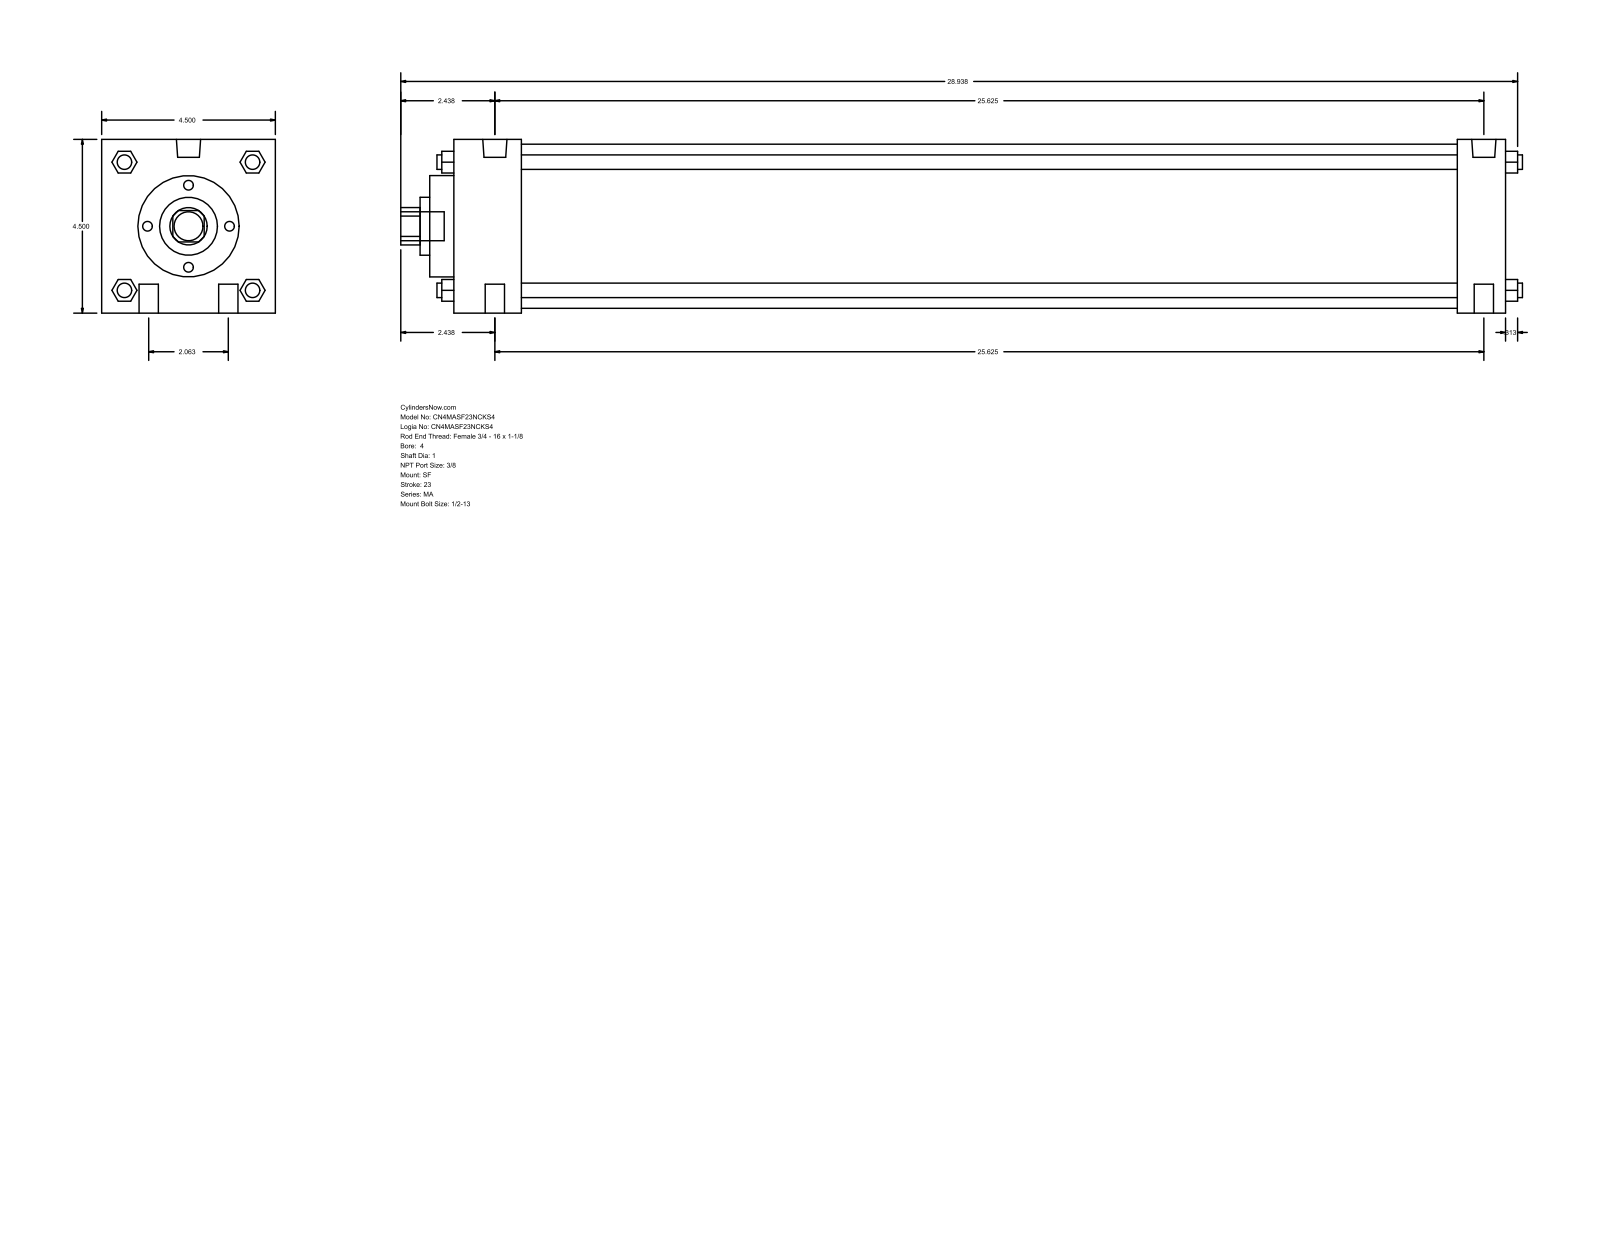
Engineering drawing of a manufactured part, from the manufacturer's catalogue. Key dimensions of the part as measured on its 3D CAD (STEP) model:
Part name (STEP PRODUCT): MA_SF__0400_1
STEP written by: GSSL Pune (CONFIG_CONTROL_DESIGN)
Units: millimetres
Bodies: 0 solids, 126 faces (95 planar, 31 cylindrical, 0 other)
Overall size (bounding box): 738.19 × 114.3 × 114.3
Round holes (diameter × count): ⌀25.4 ×1, ⌀38.1 ×1, ⌀66.67 ×1, ⌀107.95 ×1
Round bosses / shafts (diameter × count): ⌀12.7 ×4, ⌀9.53 ×4, ⌀15.93 ×2, ⌀11.11 ×2, ⌀19.05 ×1
Partial cylindrical surfaces — rounded edges, fillets, slot ends (radius × count): R12.29 ×1
Main face-to-face distances: 114.3, 692.16, 660.41, 31.75, 44.46, 615.95, 647.7, 15.87, 60.33, 676.28
